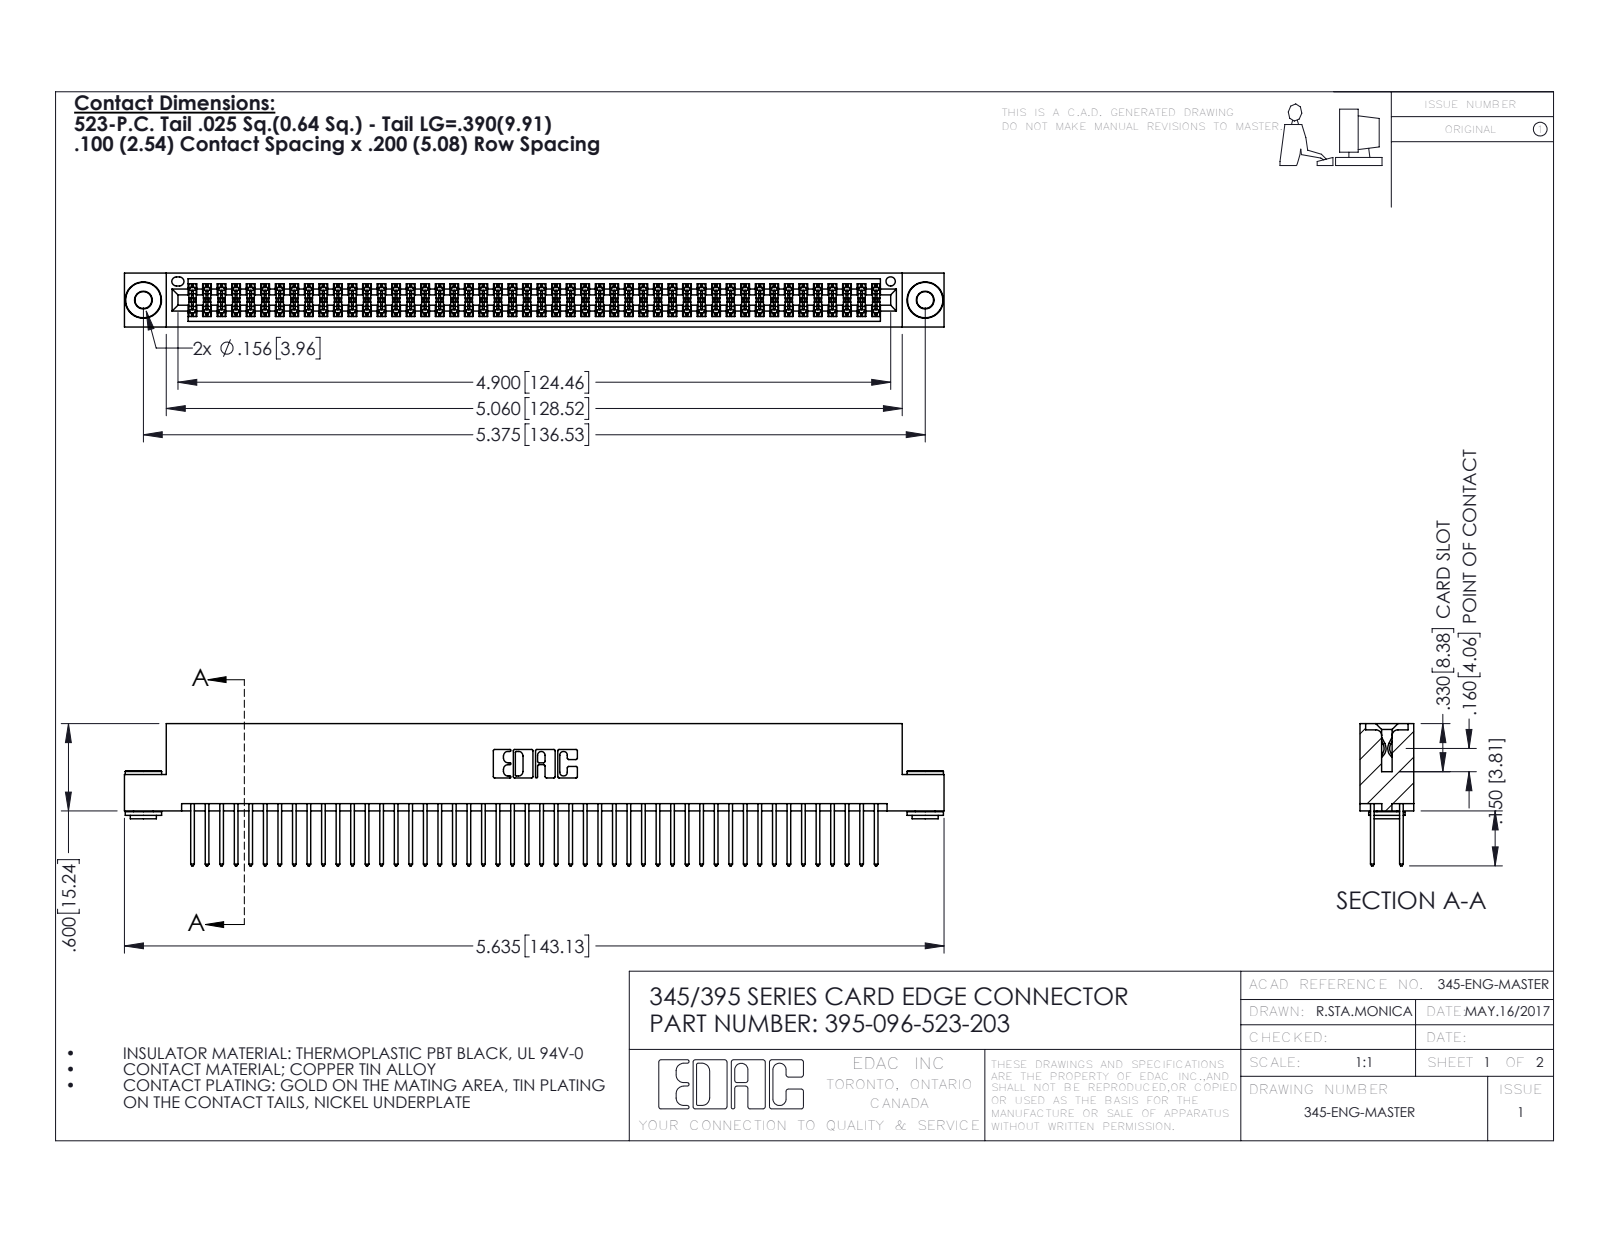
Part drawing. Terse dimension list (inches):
name: 345-292-001_345-293-123; 395-096-523-203; 345-250-002_345-250-002-102; 345 Part_Flush Mounting Lugs - 0.156 Dia-TH
written by: SolidWorks 2016 (CONFIG_CONTROL_DESIGN)
unit: in
bodies: 99 solids, 4964 faces (3258 planar, 1698 cylindrical, 8 other)
size: 5.635 × 0.977 × 0.37
volume: 0.865 in³; area: 34.34 in²
holes: 2× ⌀0.116, 2× ⌀0.156, 1× ⌀0.064
bosses: 2× ⌀0.25, 2× ⌀0.18, 2× ⌀0.136
rounds: 144× R0.006, 96× R0.01, 22× R0.01, 6× R0.007, 6× R0.031, 3× R0.026, 2× R0.014, 2× R0.019
face distances: 0.072, 0.298, 0.2, 0.025, 0.098, 0.272, 0.37, 0.225, 0.175, 0.149
hole spacings: 0.27, 5.139, 5.375
